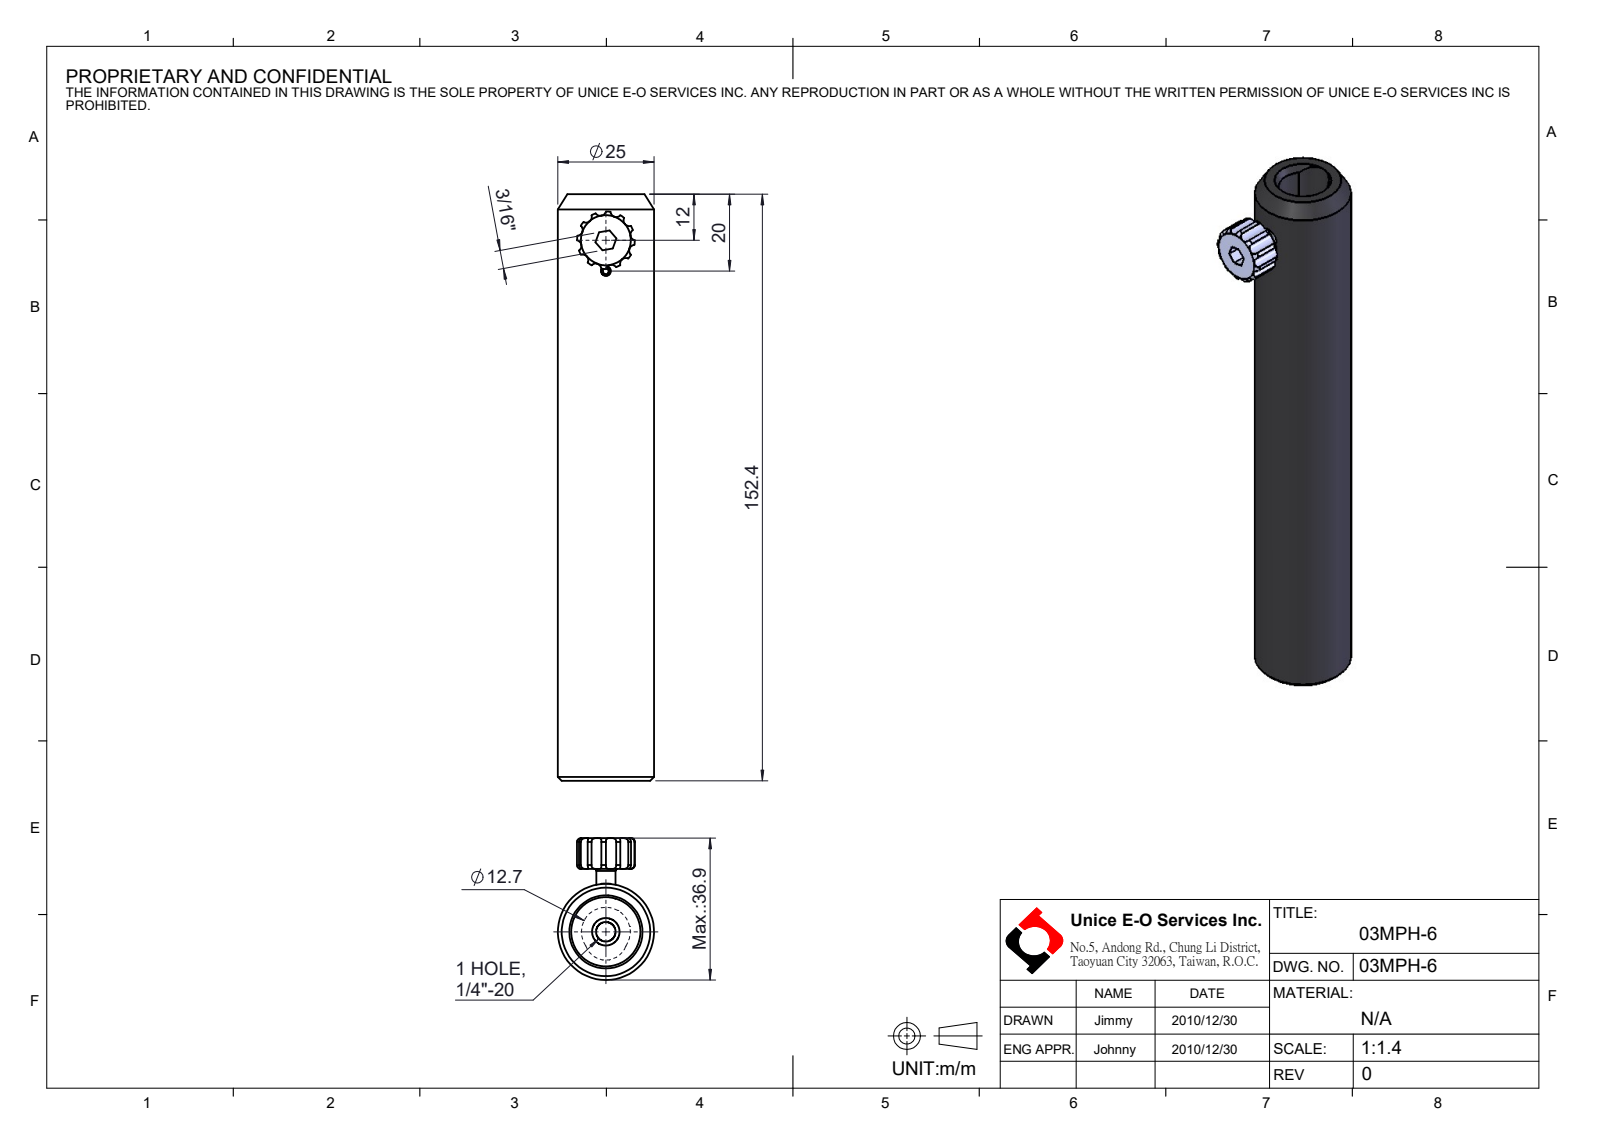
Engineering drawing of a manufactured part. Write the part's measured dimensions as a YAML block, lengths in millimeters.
part_name: "03MPH-6"
step_written_by: "SolidWorks 2016 (CONFIG_CONTROL_DESIGN)"
units: millimeters
bodies: {solids: 0, faces: 96, planar: 16, cylindrical: 42, other: 38}
overall_size: [152.4, 36.85, 25]
round_holes:
  - {diameter: 2.5, count: 1}
  - {diameter: 5.11, count: 1}
  - {diameter: 19, count: 1}
round_bosses_or_shafts:
  - {diameter: 25, count: 1}
  - {diameter: 4.94, count: 1}
partial_cylinders:
  - {radius: 1.5, count: 12}
  - {radius: 5.5, count: 1}
  - {radius: 6.35, count: 1}
  - {radius: 7.5, count: 1}
face_to_face_distances: [152.4, 8, 4.76, 4.77, 3.85, 11.85, 1.5]
